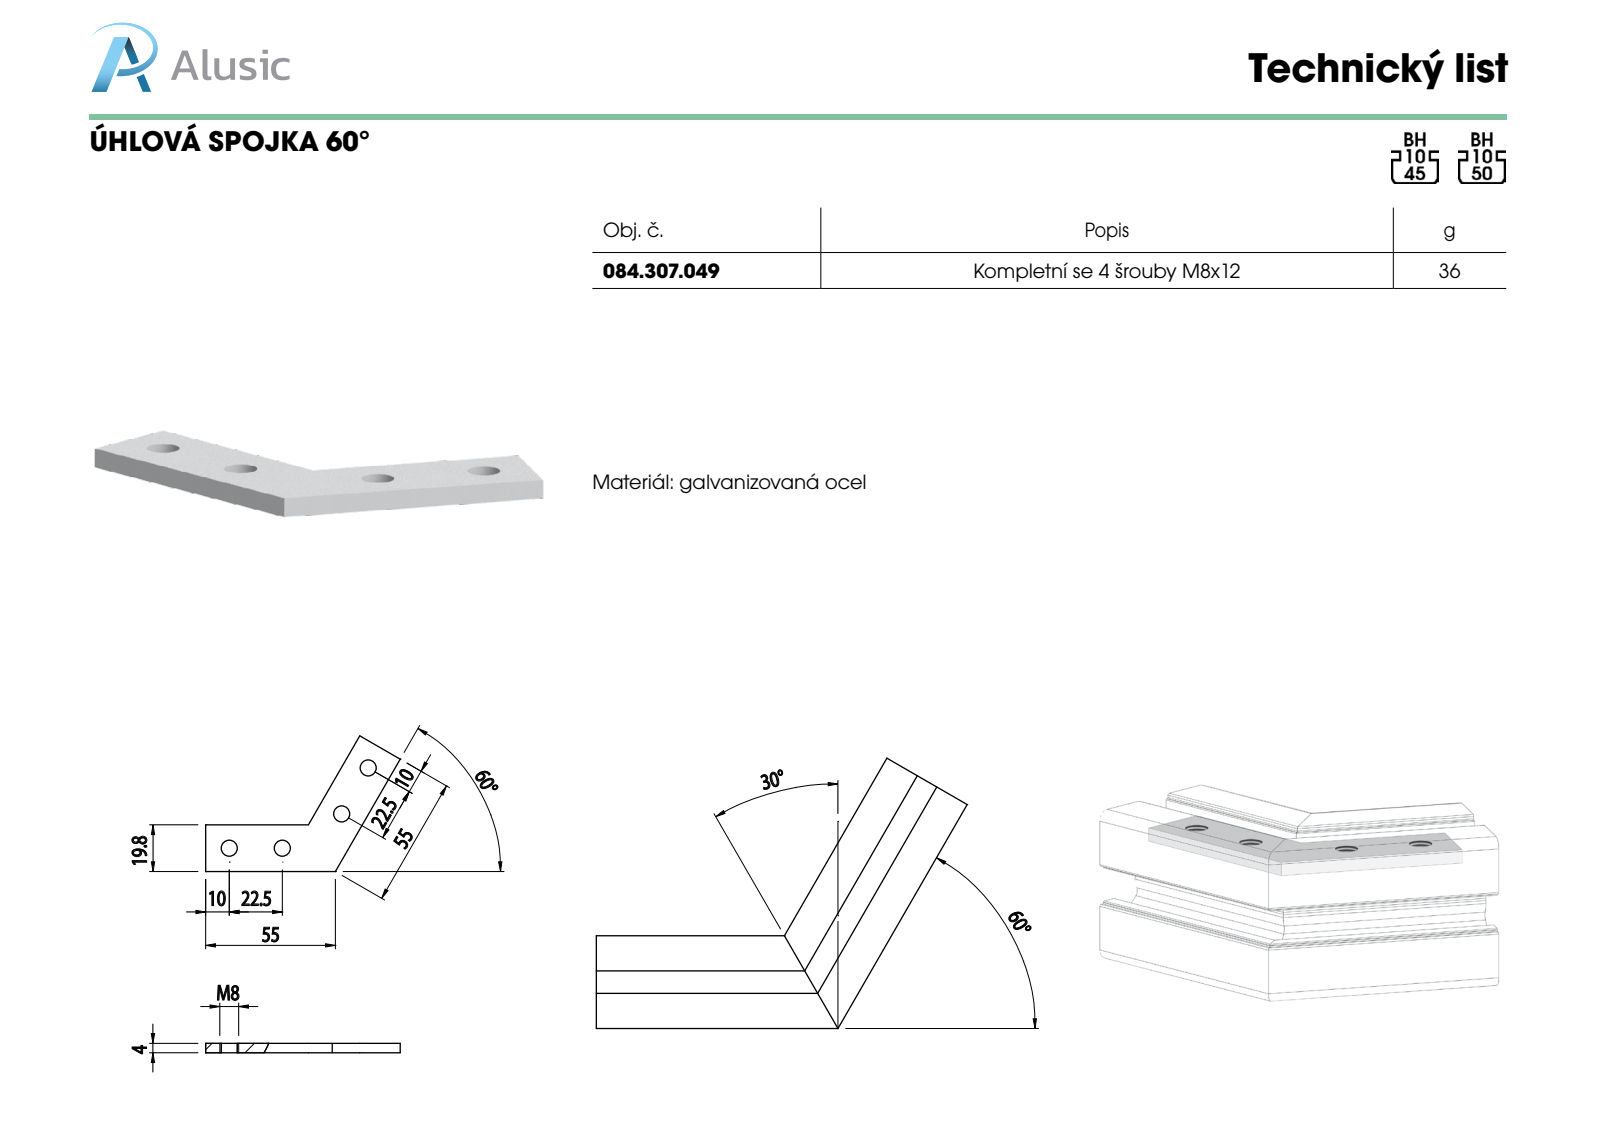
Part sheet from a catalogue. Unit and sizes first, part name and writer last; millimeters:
Units: millimetres
Overall size (bounding box): 82.5 × 57.53 × 4
Round holes (diameter × count): ⌀6.8 ×4
Main face-to-face distances: 4, 19.8
Hole centre spacings: 22.5, 29.08, 49.84, 49.85, 68.04
Volume: 7 226 mm³ · Surface area: 4 902 mm²
Bodies: 1 solid, 16 faces (8 planar, 8 cylindrical, 0 other)
Part name (STEP PRODUCT): 084.307.049
STEP written by: SolidWorks 2012 (CONFIG_CONTROL_DESIGN)
